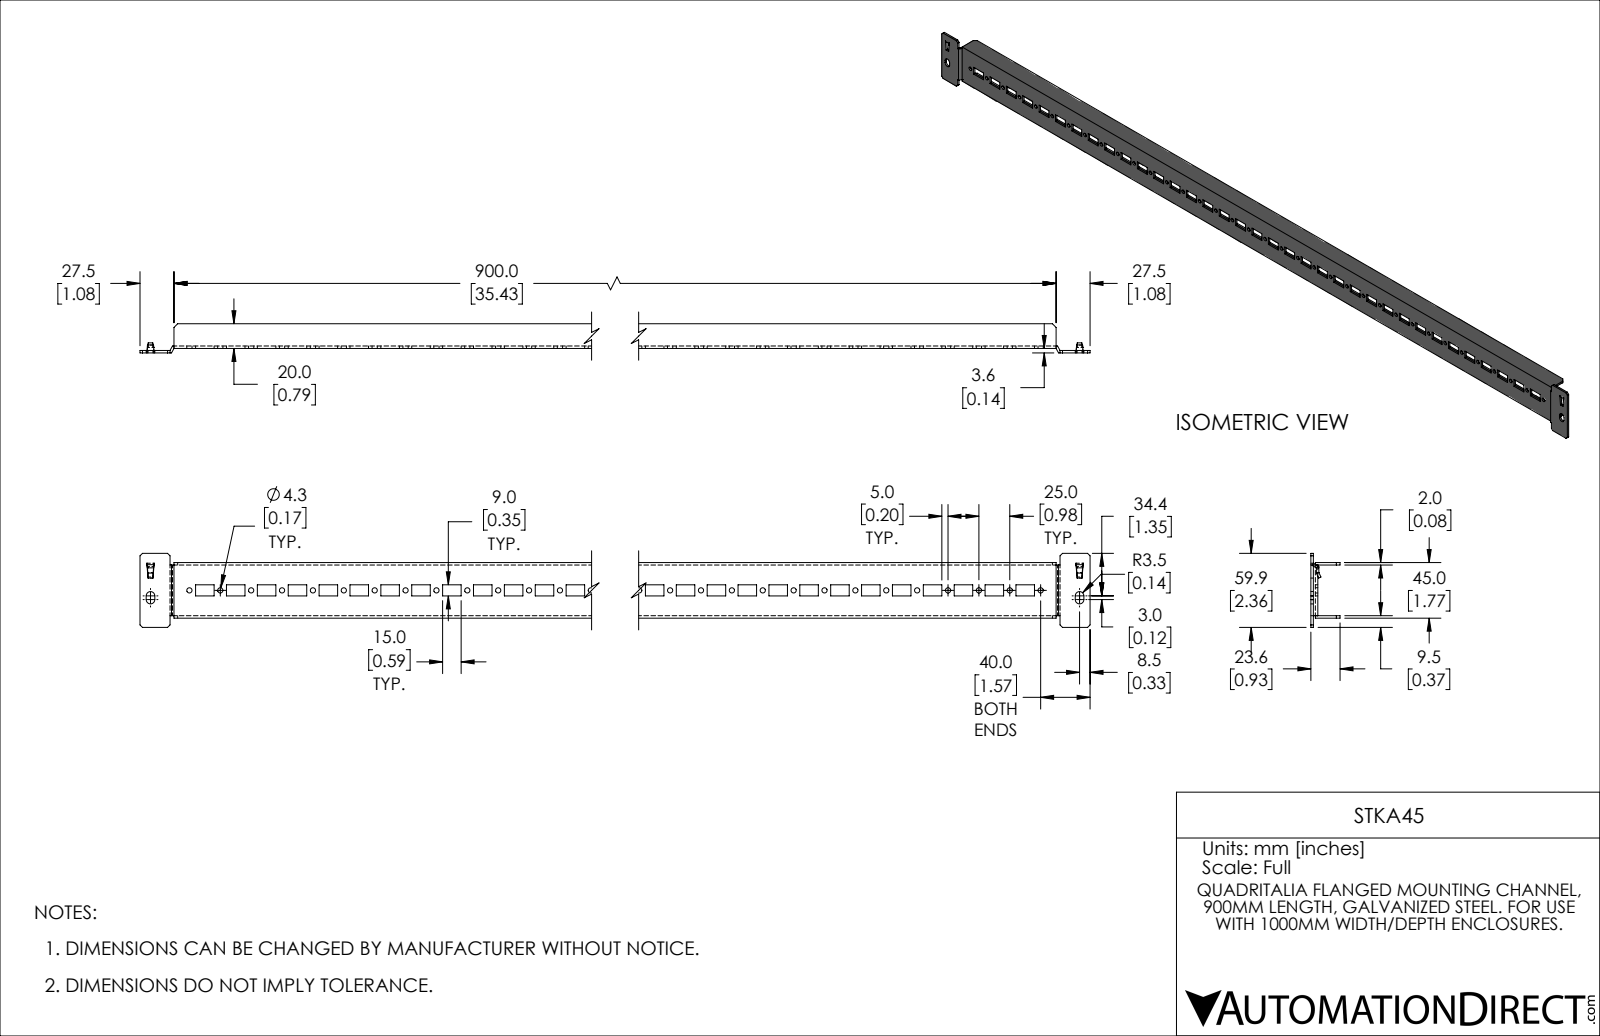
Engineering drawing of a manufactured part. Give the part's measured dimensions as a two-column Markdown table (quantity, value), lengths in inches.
| quantity | value |
| --- | --- |
| part name | STKA45 |
| STEP written by | SolidWorks 2021 (CONFIG_CONTROL_DESIGN) |
| units | inches |
| bodies | 1 solid, 286 faces (234 planar, 40 cylindrical, 12 other) |
| overall size | 37.598 × 2.359 × 0.93 |
| volume | 8.651 in³ |
| surface area | 233.6 in² |
| round holes (diameter × count) | 0.167 × 36 |
| partial cylindrical surfaces (radius × count) | 0.138 × 4 |
| main face-to-face distances | 0.079, 1.693, 1.772, 1.614, 0.709, 0.143, 0.787, 0.221, 0.93, 0.064 |
| hole center spacings | 0.984, 1.969, 2.953, 3.937, 4.921, 5.906, 6.89, 7.874 |
